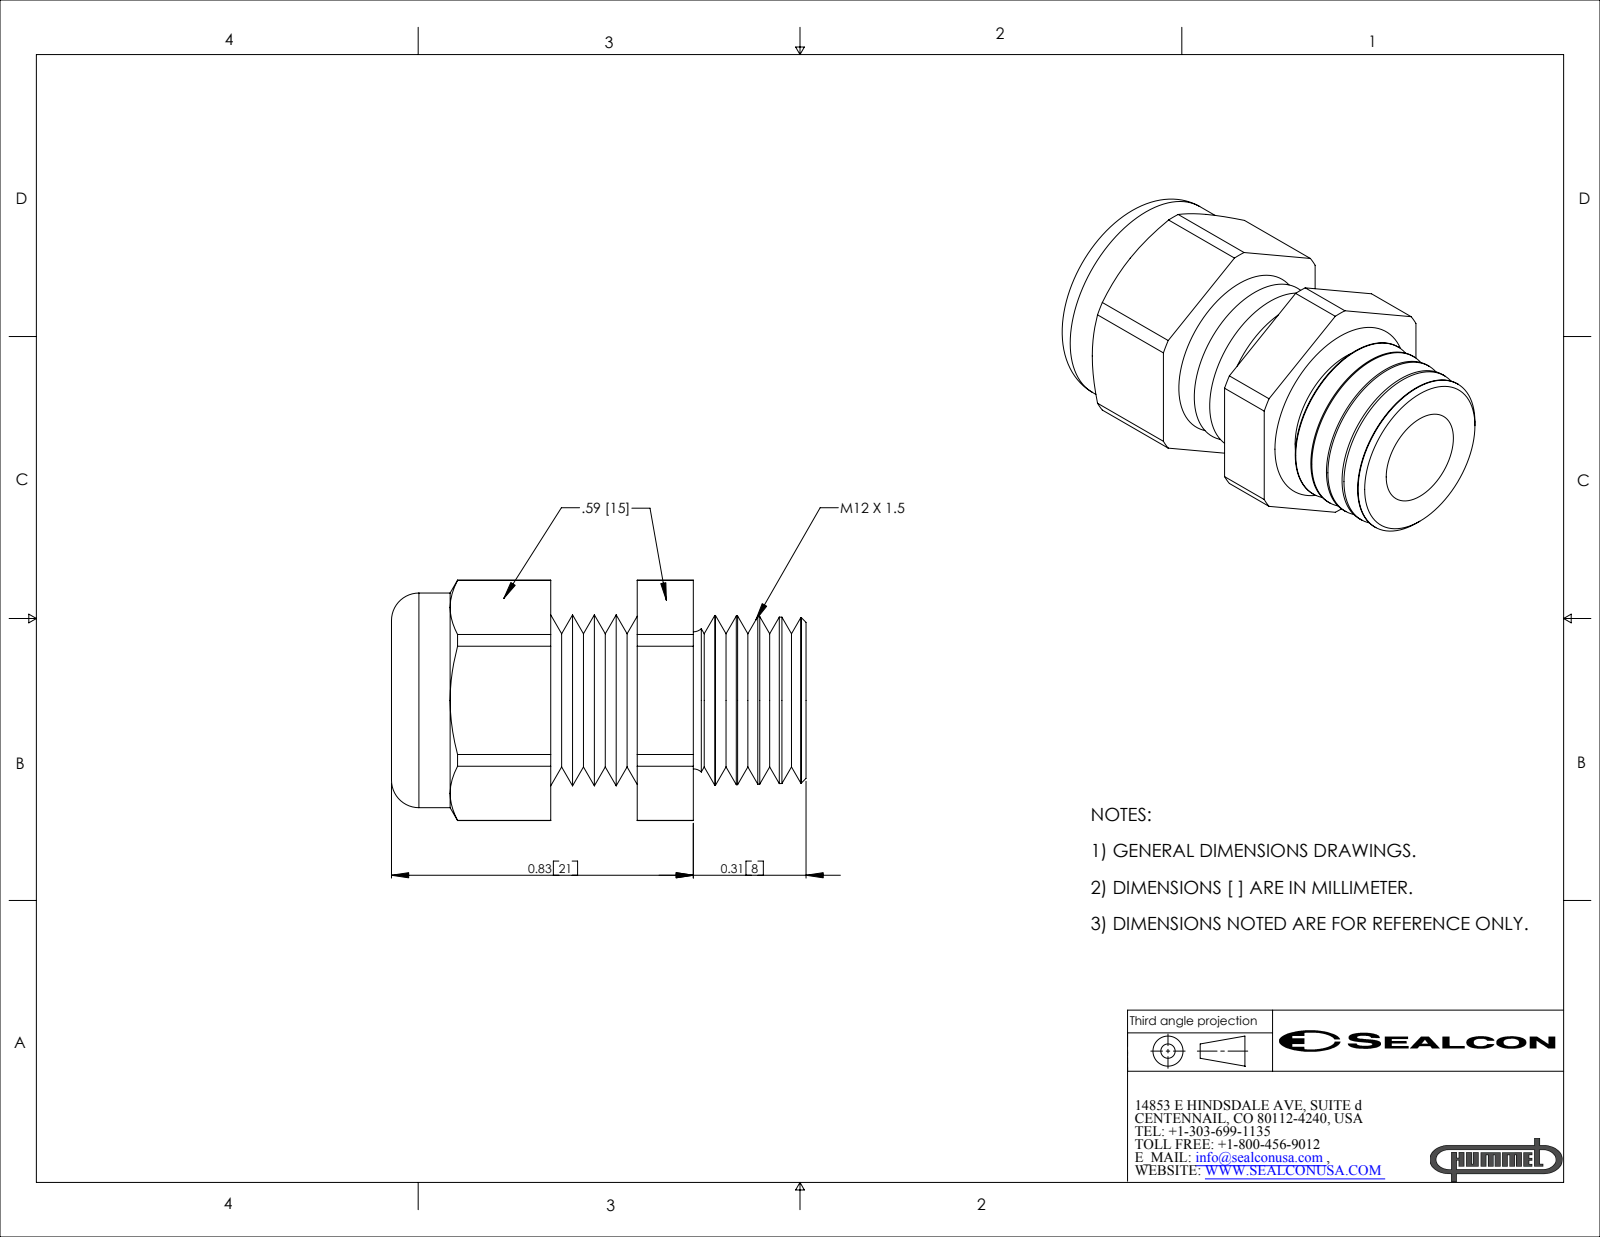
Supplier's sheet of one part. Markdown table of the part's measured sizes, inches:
| quantity | value |
| --- | --- |
| part name | CD12MR |
| STEP written by | SolidWorks 2007 (CONFIG_CONTROL_DESIGN) |
| units | inches |
| bodies | 2 solids, 108 faces (20 planar, 24 cylindrical, 64 other) |
| overall size | 1.14 × 0.661 × 0.59 |
| volume | 0.198 in³ |
| surface area | 4.637 in² |
| round holes (diameter × count) | 0.2 × 1, 0.4 × 1, 0.47 × 1 |
| round bosses / shafts (diameter × count) | 0.59 × 1 |
| partial cylindrical surfaces (radius × count) | 0.33 × 1 |
| main face-to-face distances | 0.59, 0.515, 0.277, 0.238, 0.669, 0.392, 0.154, 0.979, 0.702, 0.464 |
